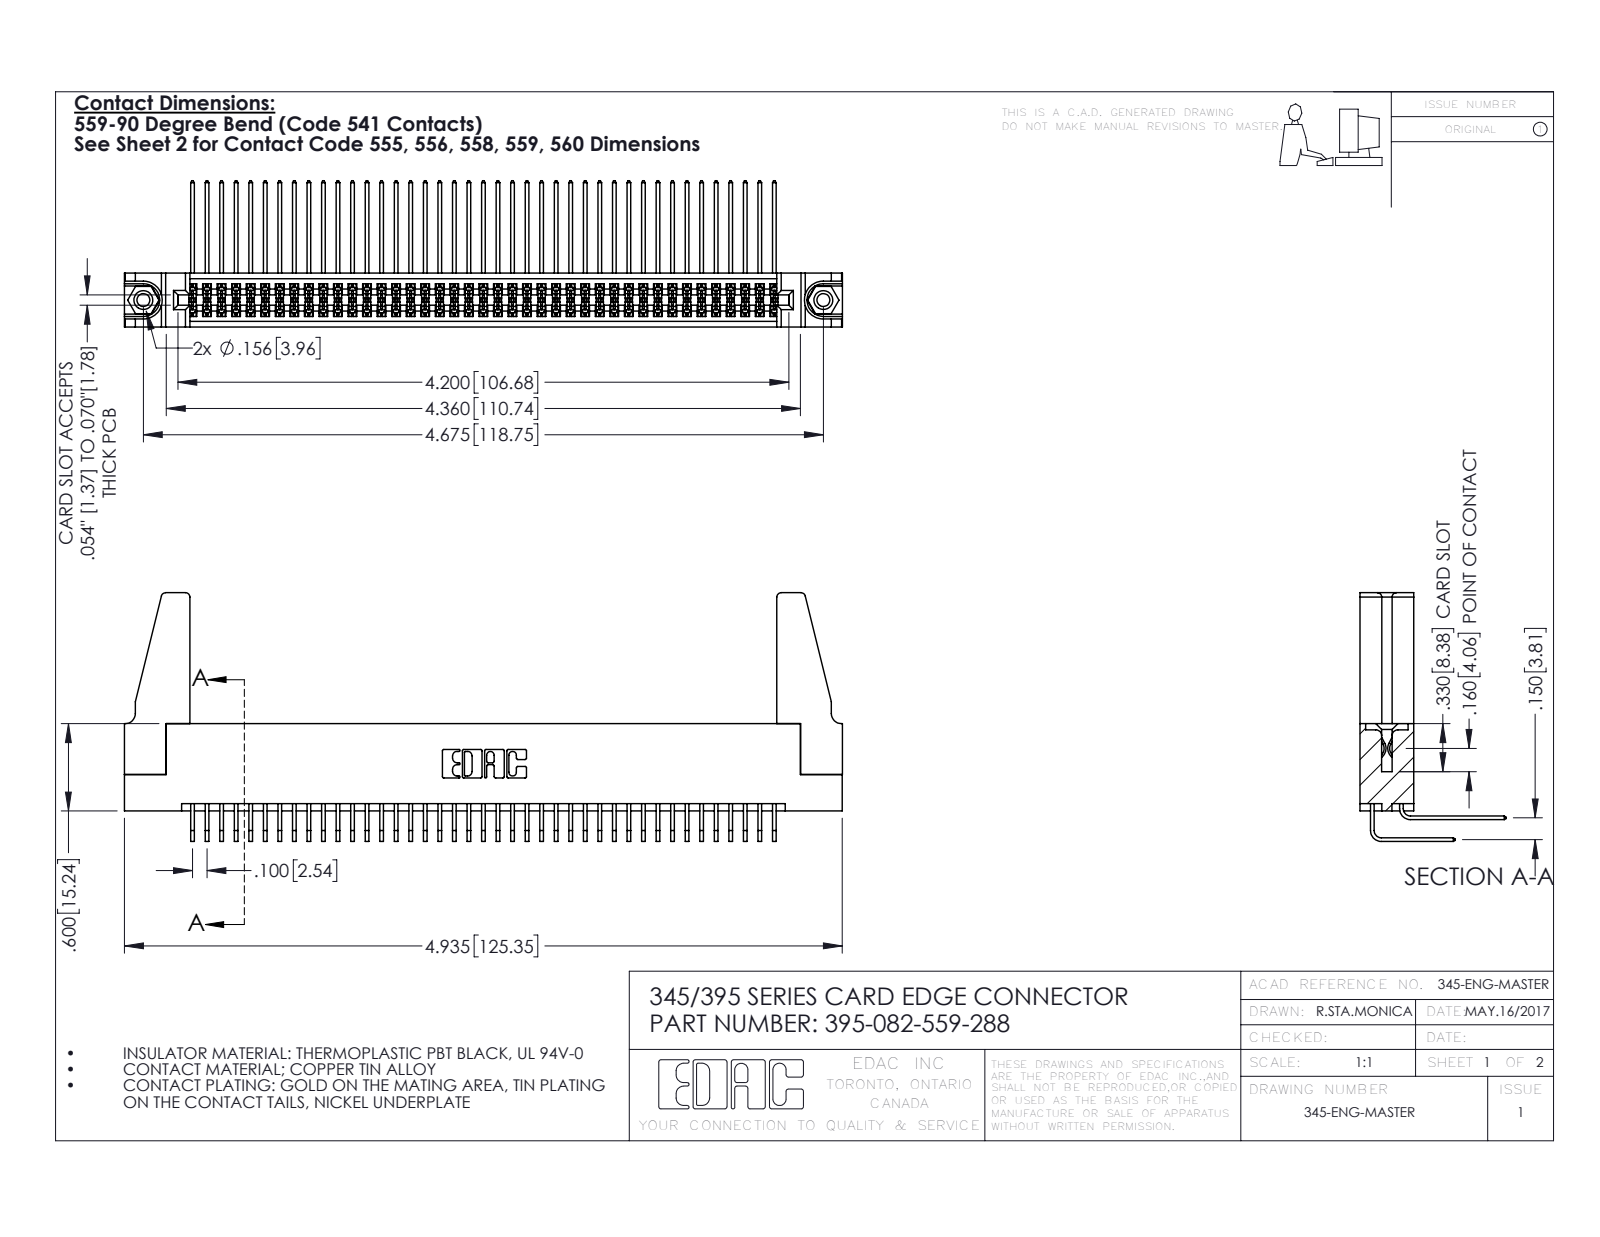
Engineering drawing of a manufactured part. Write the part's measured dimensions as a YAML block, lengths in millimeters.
part_name: "345 Part_Flush Mounting Lugs - 0.156 Dia-TH; 345-250-001_345-250-001-102; 345-292-001_558 559 Tail - 1; 395-082-559-288 (+2 more)"
step_written_by: "SolidWorks 2016 (CONFIG_CONTROL_DESIGN)"
units: millimeters
bodies: {solids: 87, faces: 4514, planar: 3022, cylindrical: 1476, other: 16}
overall_size: [125.4, 43.4, 25.5]
volume: 15900
surface_area: 24010
round_holes:
  - {diameter: 2.3, count: 2}
  - {diameter: 3.2, count: 2}
  - {diameter: 4, count: 2}
  - {diameter: 1.6, count: 1}
round_bosses_or_shafts:
  - {diameter: 3.9, count: 2}
partial_cylinders:
  - {radius: 0.2, count: 123}
  - {radius: 0.3, count: 22}
  - {radius: 0.8, count: 8}
  - {radius: 0.2, count: 6}
  - {radius: 0.8, count: 6}
  - {radius: 0.7, count: 3}
  - {radius: 0.4, count: 2}
  - {radius: 0.5, count: 2}
face_to_face_distances: [1.8, 7.6, 9.4, 5.1, 2.5, 6.9, 0.6, 5.7, 4.4, 3.8]
hole_center_spacings: [6.9, 112.8, 118.7]
